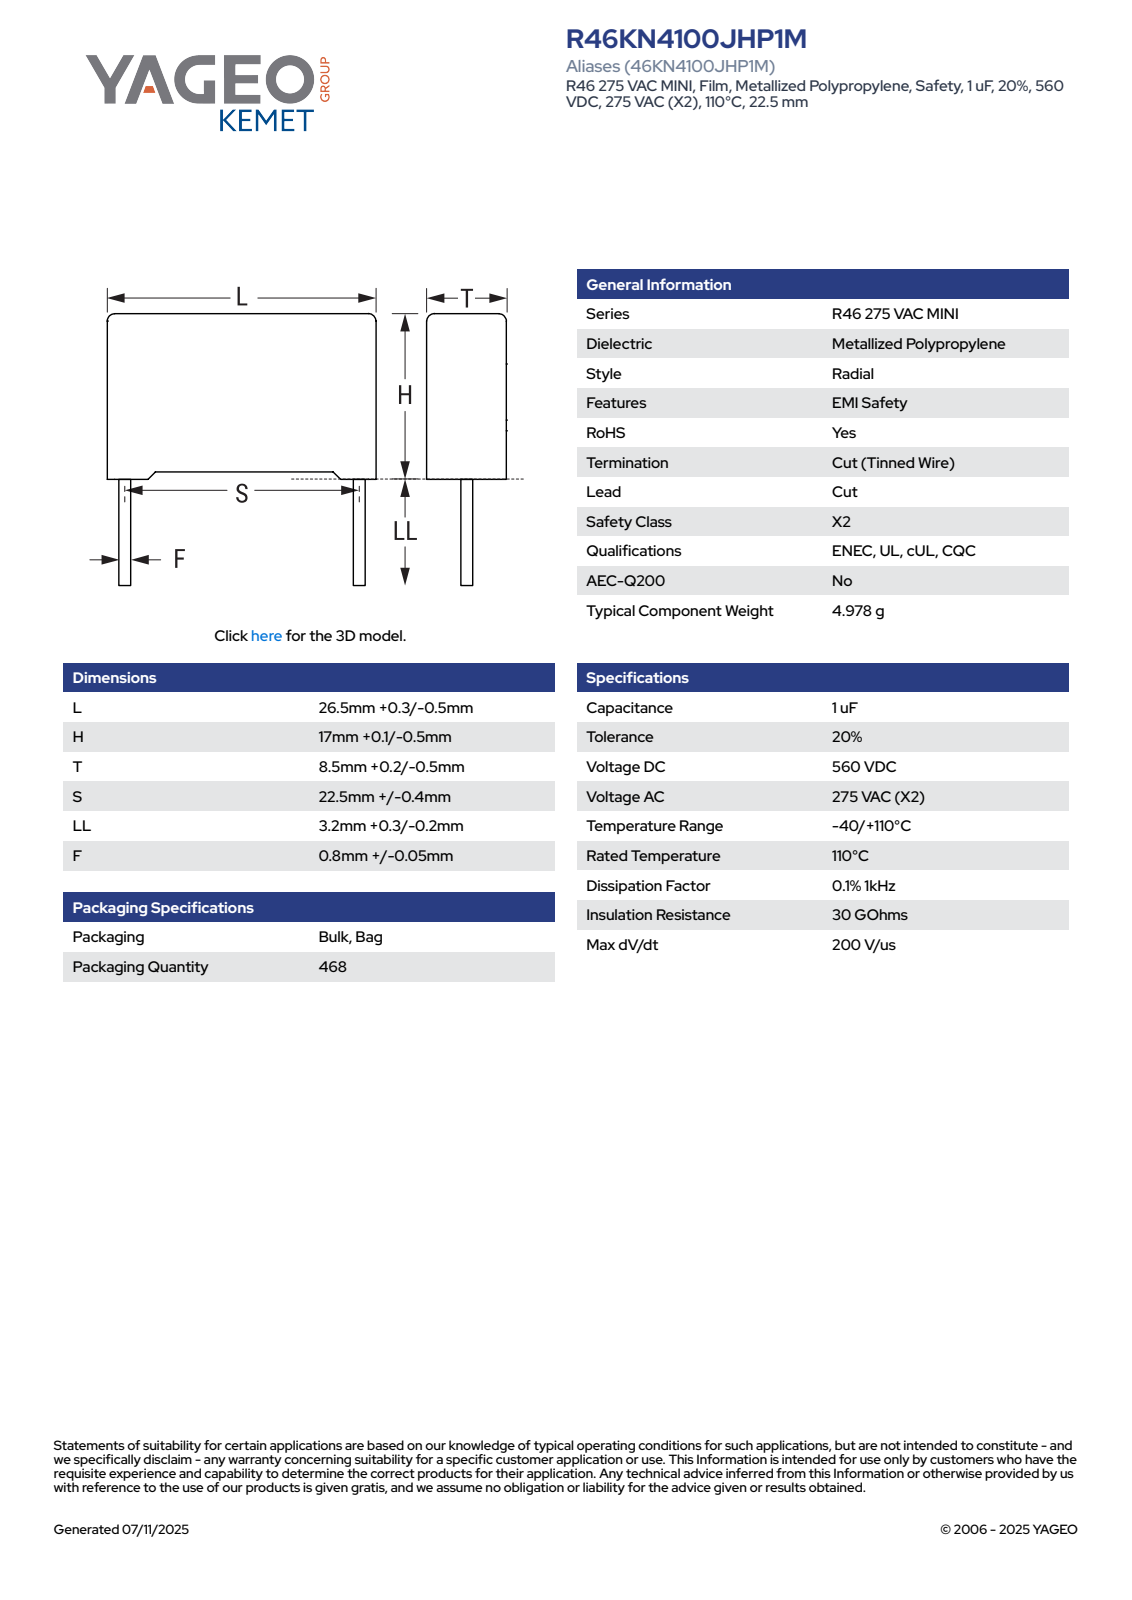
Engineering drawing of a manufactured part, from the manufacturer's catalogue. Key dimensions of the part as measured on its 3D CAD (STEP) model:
Part name (STEP PRODUCT): CFR_RB2_26.5X17X8.5_L26.8H17.1T8.7S22.5LL3.5F0.85
STEP written by: SolidWorks 2021 (AUTOMOTIVE_DESIGN)
Units: millimetres
Bodies: 4 solids, 85 faces (77 planar, 8 cylindrical, 0 other)
Overall size (bounding box): 26.8 × 20.6 × 8.71
Volume: 3 839 mm³ · Surface area: 1 746 mm²
Round bosses / shafts (diameter × count): ⌀0.85 ×2
Partial cylindrical surfaces — rounded edges, fillets, slot ends (radius × count): R0.5 ×4
Main face-to-face distances: 8.7, 16.35, 26.8, 16.51, 0.89, 0.75, 0.59, 17.1, 7.81, 8.71
